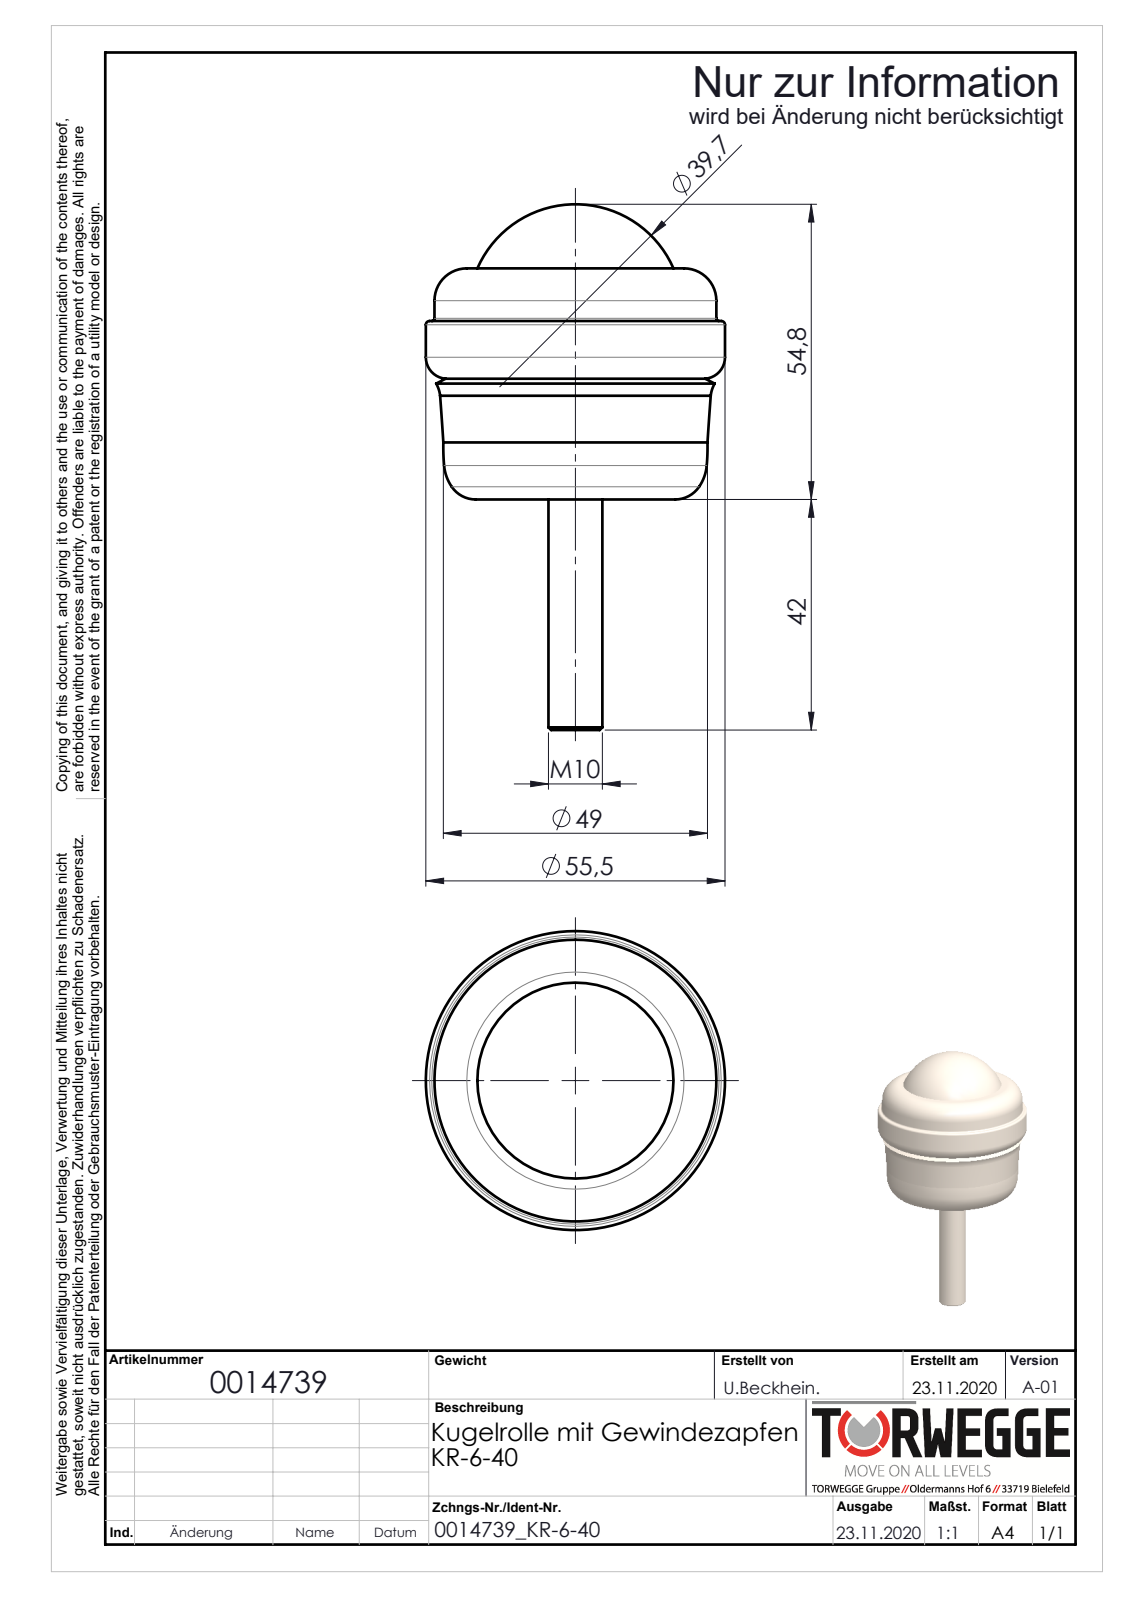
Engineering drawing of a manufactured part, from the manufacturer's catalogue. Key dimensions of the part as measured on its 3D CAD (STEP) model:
Part name (STEP PRODUCT): 0014739
STEP written by: SolidWorks 2018 (AUTOMOTIVE_DESIGN)
Units: millimetres
Bodies: 1 solid, 35 faces (3 planar, 6 cylindrical, 26 other)
Overall size (bounding box): 97.6 × 55.5 × 55.5
Volume: 95 405 mm³ · Surface area: 12 759 mm²
Round bosses / shafts (diameter × count): ⌀55.5 ×1, ⌀52.3 ×1, ⌀10 ×1
Main face-to-face distances: 9.77, 75.93, 85.7
